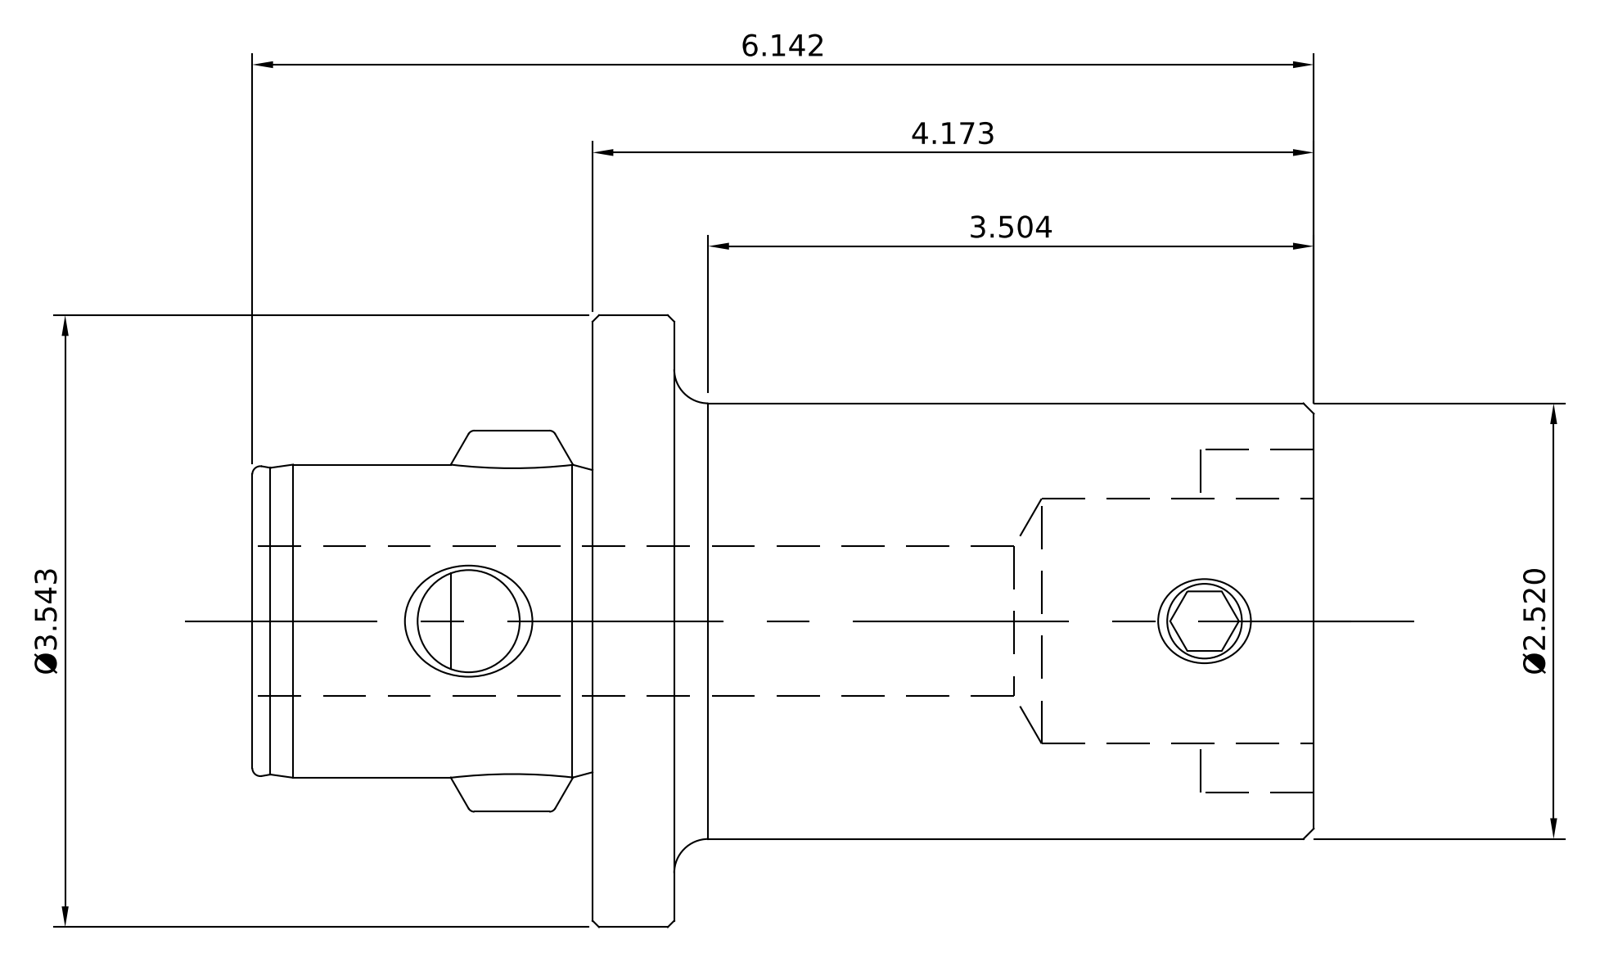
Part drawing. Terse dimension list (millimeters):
name: 10.690.43X_10.690.436; 10.691.50X_10.691.507; 691-50XRing_10.691.507Ring; 11.332.760 (+1 more)
written by: SolidWorks 2014 (AUTOMOTIVE_DESIGN)
unit: mm
bodies: 4 solids, 154 faces (43 planar, 53 cylindrical, 58 other)
size: 156 × 90 × 90
volume: 363 842 mm³; area: 59 894 mm²
holes: 1× ⌀7.5, 1× ⌀10.2, 1× ⌀12.3, 1× ⌀15, 1× ⌀18, 1× ⌀21, 1× ⌀22, 1× ⌀24.7, 1× ⌀26, 1× ⌀33, 1× ⌀36, 1× ⌀36.5
bosses: 2× ⌀12, 1× ⌀90, 1× ⌀63.27, 1× ⌀62.87, 1× ⌀46, 1× ⌀17.9, 1× ⌀15.9
rounds: 2× R5.5, 1× R23
face distances: 12, 106, 94, 50, 62, 156, 111, 61, 49, 45
hole spacings: 25, 108.15
